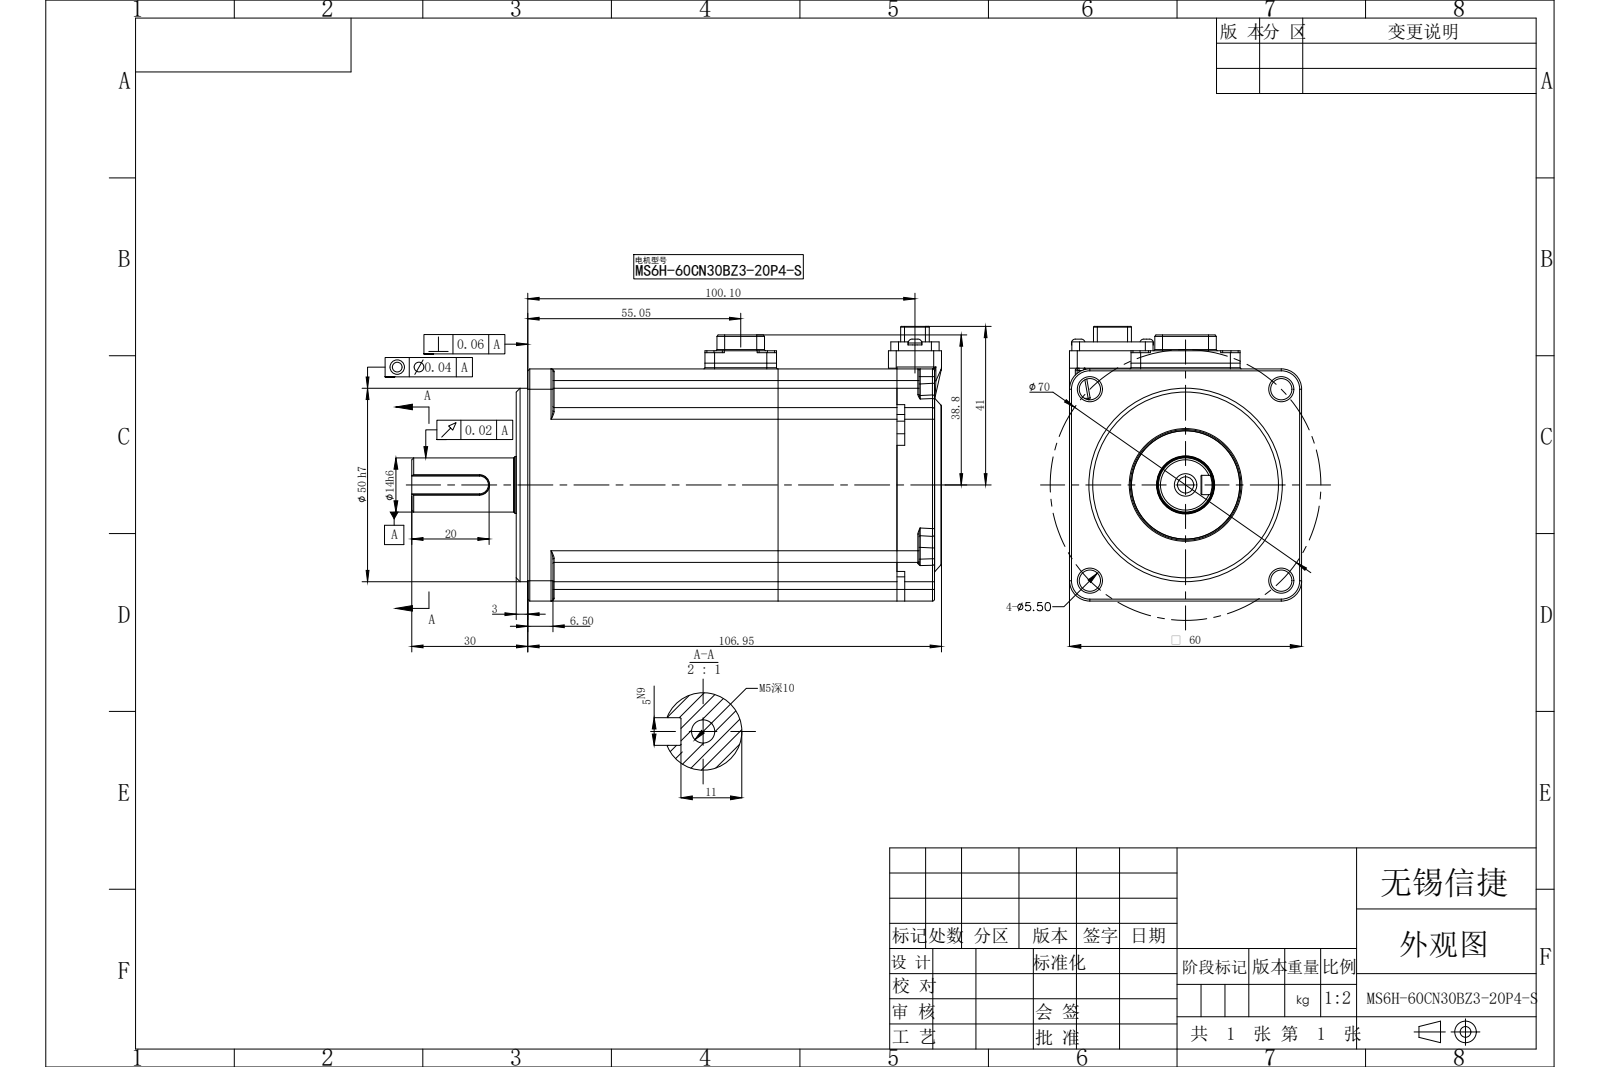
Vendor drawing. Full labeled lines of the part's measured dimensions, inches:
Part name (STEP PRODUCT): MS6H-60CN30BZ3-20P4-S
STEP written by: SolidWorks 2022 (CONFIG_CONTROL_DESIGN)
Units: inches
Bodies: 0 solids, 738 faces (292 planar, 261 cylindrical, 185 other)
Overall size (bounding box): 5.392 × 2.795 × 2.362
Round holes (diameter × count): ⌀0.083 ×8, ⌀0.134 ×4, ⌀0.217 ×4, ⌀0.138 ×3, ⌀0.063 ×2, ⌀0.165 ×1, ⌀0.591 ×1
Round bosses / shafts (diameter × count): ⌀0.138 ×2, ⌀1.969 ×1, ⌀1.102 ×1, ⌀0.583 ×1, ⌀0.551 ×1
Partial cylindrical surfaces — rounded edges, fillets, slot ends (radius × count): R0.02 ×41, R0.012 ×36, R0.008 ×23, R0.118 ×17, R0.079 ×16, R0.039 ×5, R0.098 ×5, R0.024 ×4
Main face-to-face distances: 2.362, 2.547, 1.969, 0.394, 3.876, 0.453, 4.329, 4.211, 3.758, 0.118
Hole centre spacings: 0.272, 0.332, 0.964, 1.229, 1.378, 1.626, 1.738, 1.949
